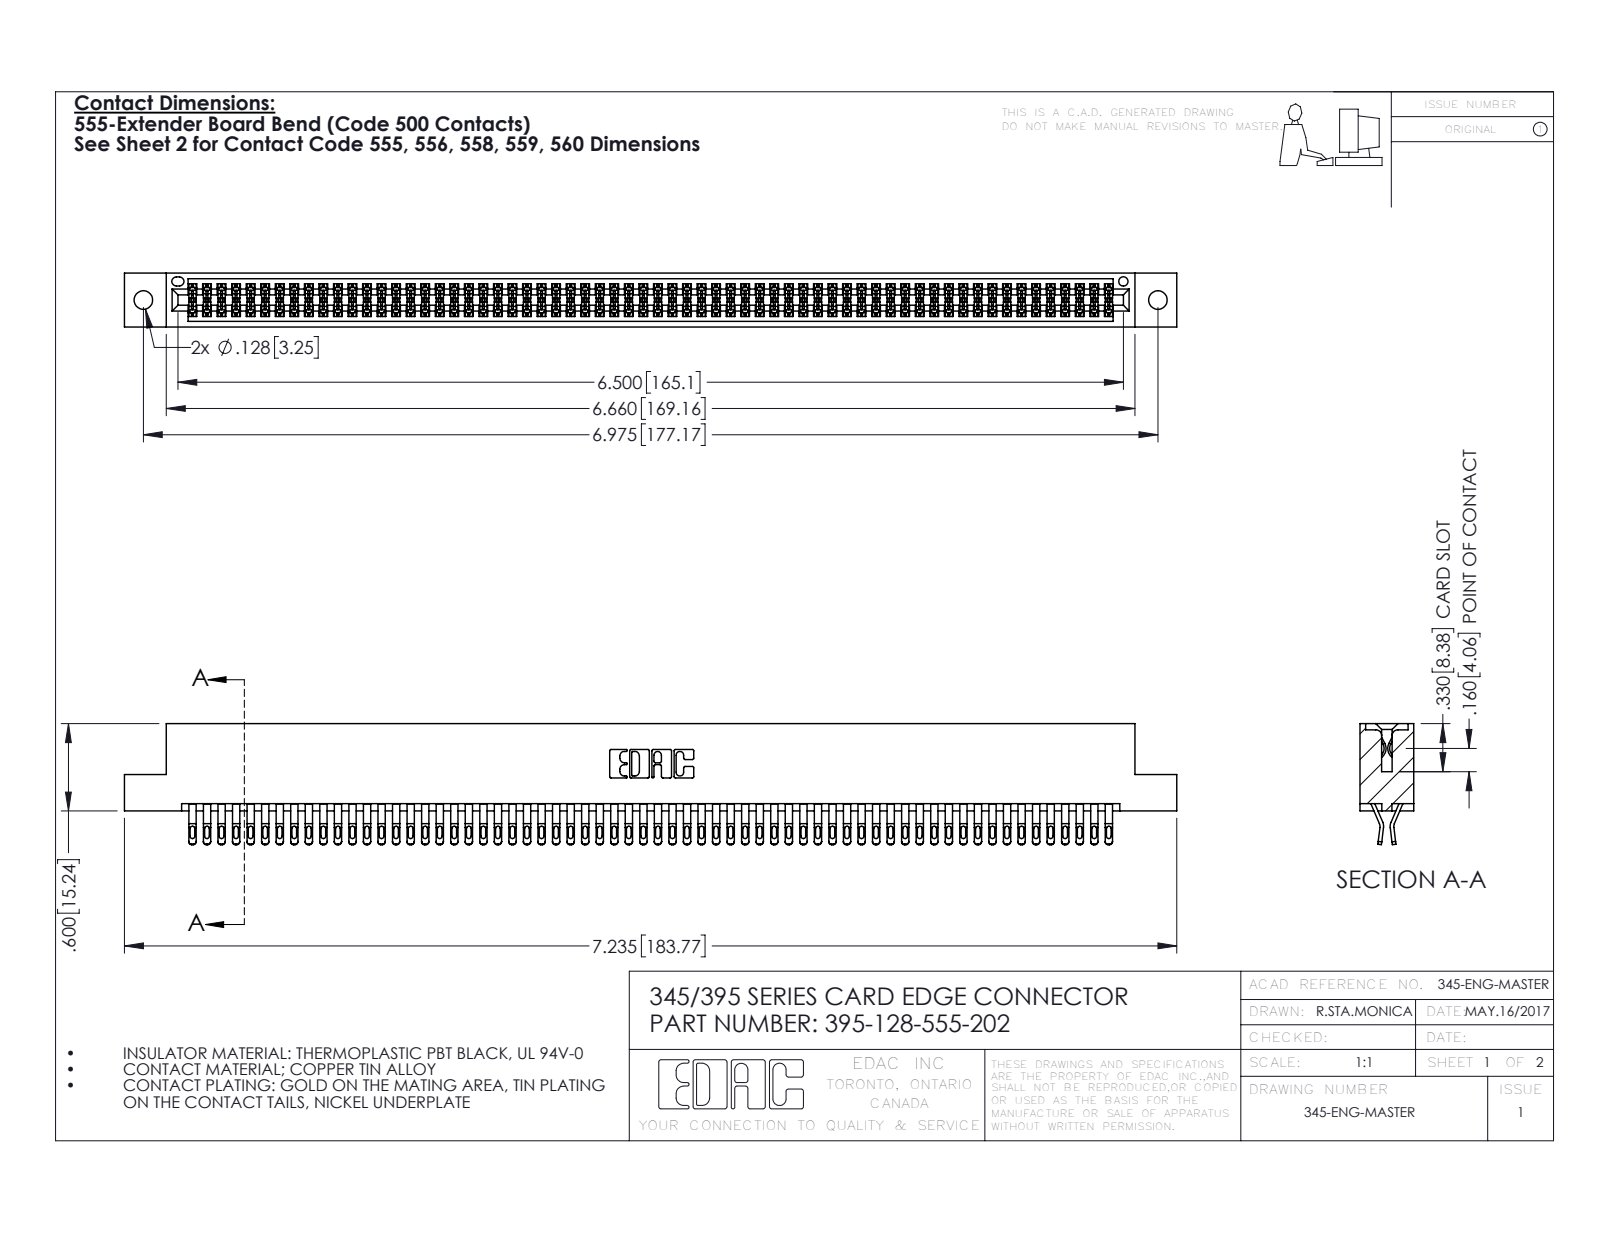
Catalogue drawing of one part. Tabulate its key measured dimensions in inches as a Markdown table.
| quantity | value |
| --- | --- |
| part name | 345 Part_Flush Mounting Lugs - 0.128 Dia; 345-292-001_555 Tail; 395-128-555-202 |
| STEP written by | SolidWorks 2016 (CONFIG_CONTROL_DESIGN) |
| units | inches |
| bodies | 129 solids, 7294 faces (4048 planar, 3246 cylindrical, 0 other) |
| overall size | 7.235 × 0.832 × 0.37 |
| volume | 1.122 in³ |
| surface area | 44.37 in² |
| round holes (diameter × count) | 0.128 × 2, 0.064 × 1 |
| partial cylindrical surfaces (radius × count) | 0.016 × 320, 0.02 × 256, 0.006 × 192, 0.01 × 22, 0.007 × 6, 0.031 × 6, 0.026 × 3, 0.01 × 2 |
| main face-to-face distances | 0.298, 0.072, 0.025, 0.37, 0.2, 0.098, 0.272, 0.225, 0.175, 0.149 |
| hole center spacings | 0.27, 6.739, 6.975 |
